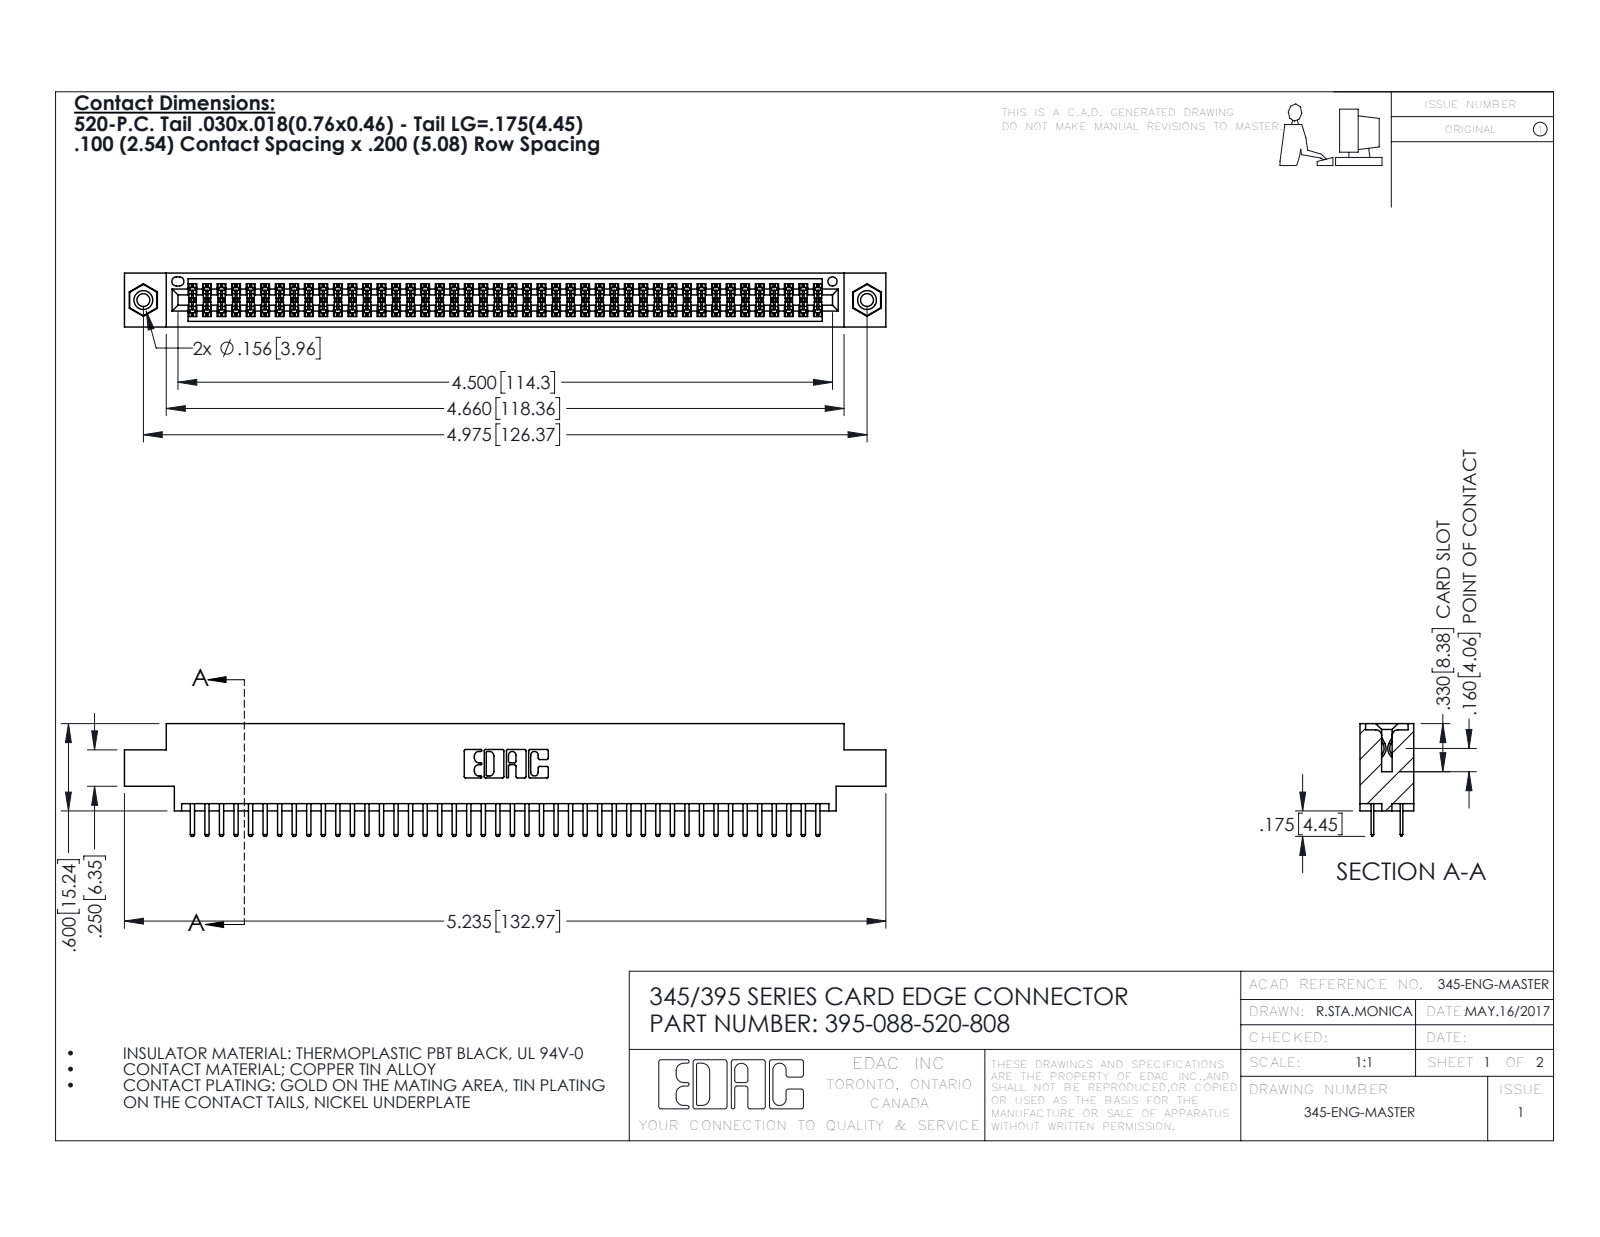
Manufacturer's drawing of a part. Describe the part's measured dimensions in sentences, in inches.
The part is named "345-250-001_345-250-003-102; 345 Part_0.170 Offset - 0.156 Dia-TI; 395-088-520-808; 345-292-001_345-293-120". Its 3-D file was written by "SolidWorks 2016 (CONFIG_CONTROL_DESIGN)". It is 91 solids with 4942 faces: 3196 planar, 1730 cylindrical and 16 other. Overall it measures 5.235 by 0.775 by 0.37 inches. Its volume is 0.78 cubic inches and its surface area 29.45 square inches. Round holes: 2 of diameter 0.089, 2 of diameter 0.125, 2 of diameter 0.156, 1 of diameter 0.064. Round bosses or shafts: 2 of diameter 0.155. Partial cylindrical surfaces (rounded edges, fillets, slot ends): 132 of radius 0.006, 92 of radius 0.01, 22 of radius 0.01, 6 of radius 0.007, 6 of radius 0.031, 3 of radius 0.026, 2 of radius 0.014, 2 of radius 0.019. The main face-to-face distances are 0.072, 0.298, 0.2, 0.37, 0.098, 0.272, 0.025, 0.225, 0.022, 0.175. The hole center spacings are 0.27, 4.739, 4.975.
